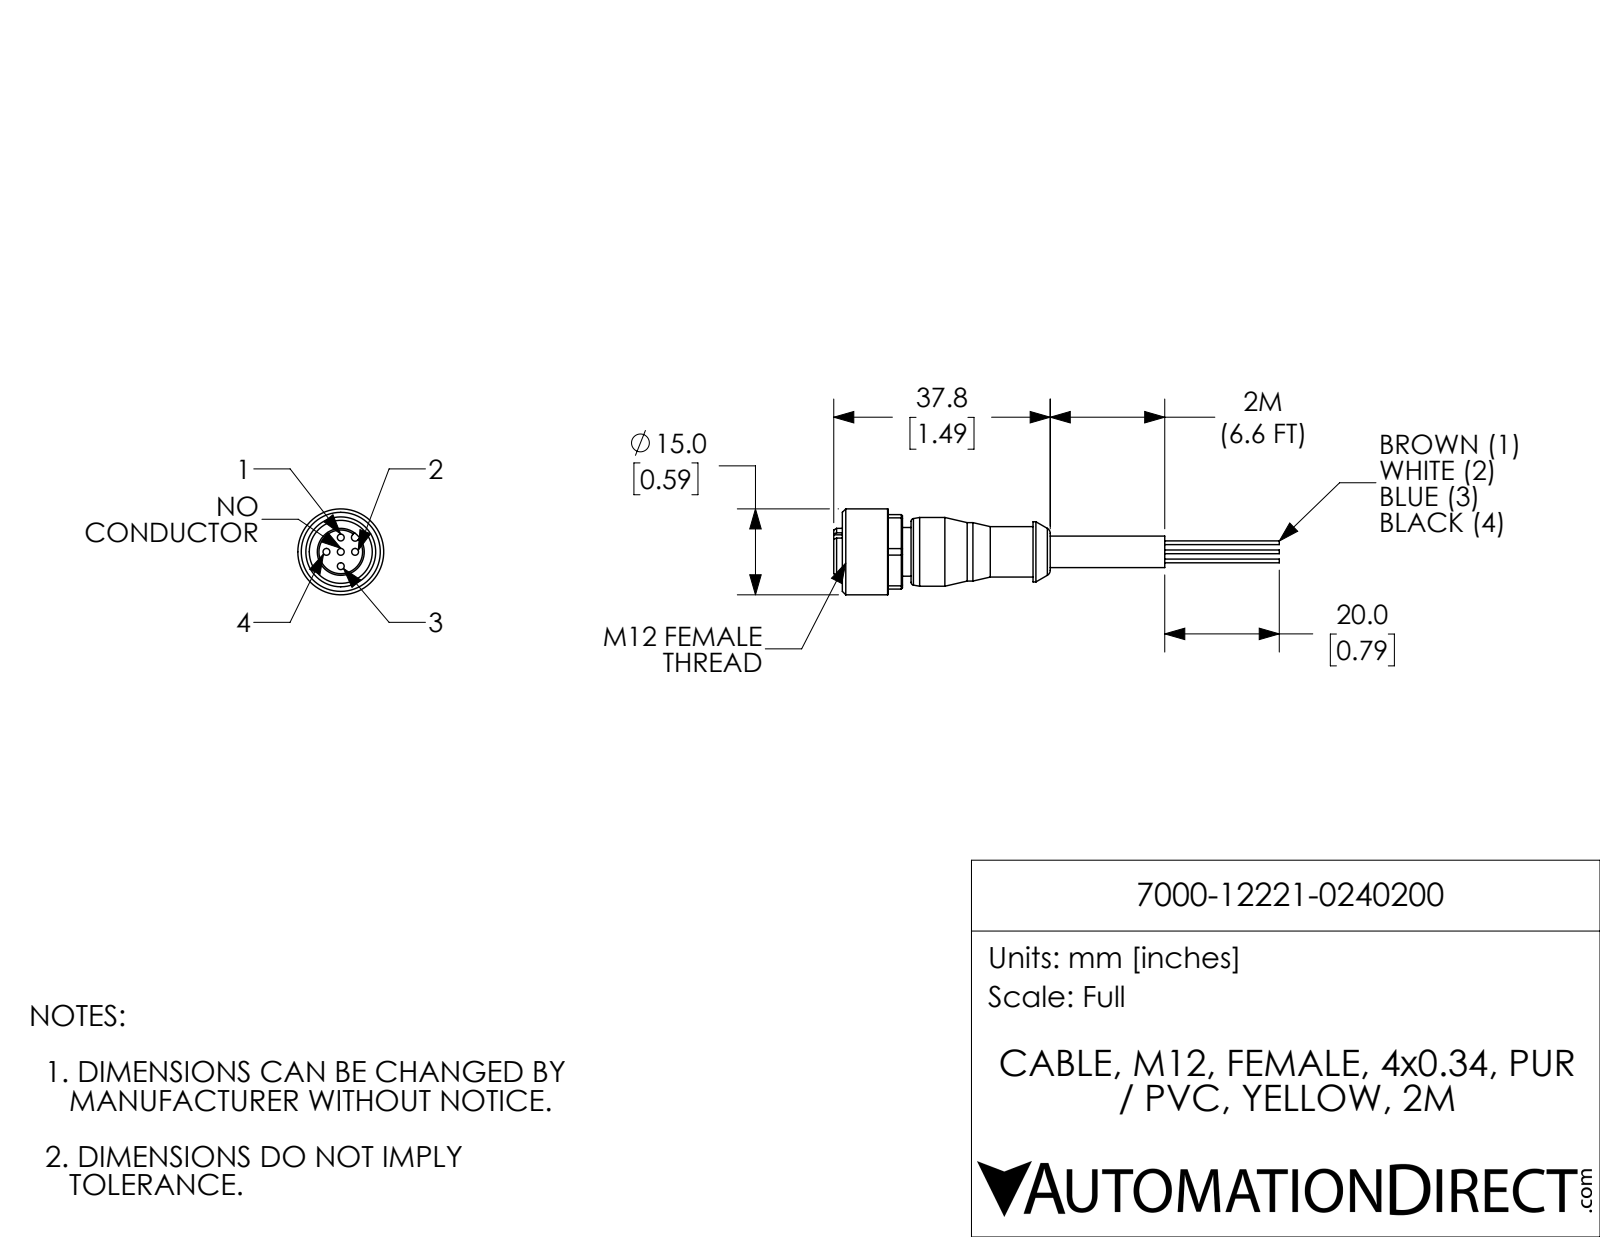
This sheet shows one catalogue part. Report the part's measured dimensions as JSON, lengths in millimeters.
{"part_name": "7000-12221-0240200", "step_written_by": "SolidWorks 2017 (AUTOMOTIVE_DESIGN)", "units": "millimeters", "bodies": {"solids": 1, "faces": 103, "planar": 33, "cylindrical": 43, "other": 27}, "overall_size": [77.8, 15, 15], "volume_mm3": 4050, "surface_area_mm2": 2830, "round_holes": [[1.2, 5], [11, 1]], "round_bosses_or_shafts": [[0.7, 4], [15, 1], [12, 1], [10.5, 1], [10.2, 1], [8.8, 1], [8.5, 1], [8.2, 1]], "partial_cylinders_radius": [[0.7, 1], [7.2, 1]], "face_to_face_distances": [12, 1.5, 3, 13, 9, 25.8, 7.5, 10.5, 2.5, 13.5], "hole_center_spacings": [2.5, 3.5, 5]}
